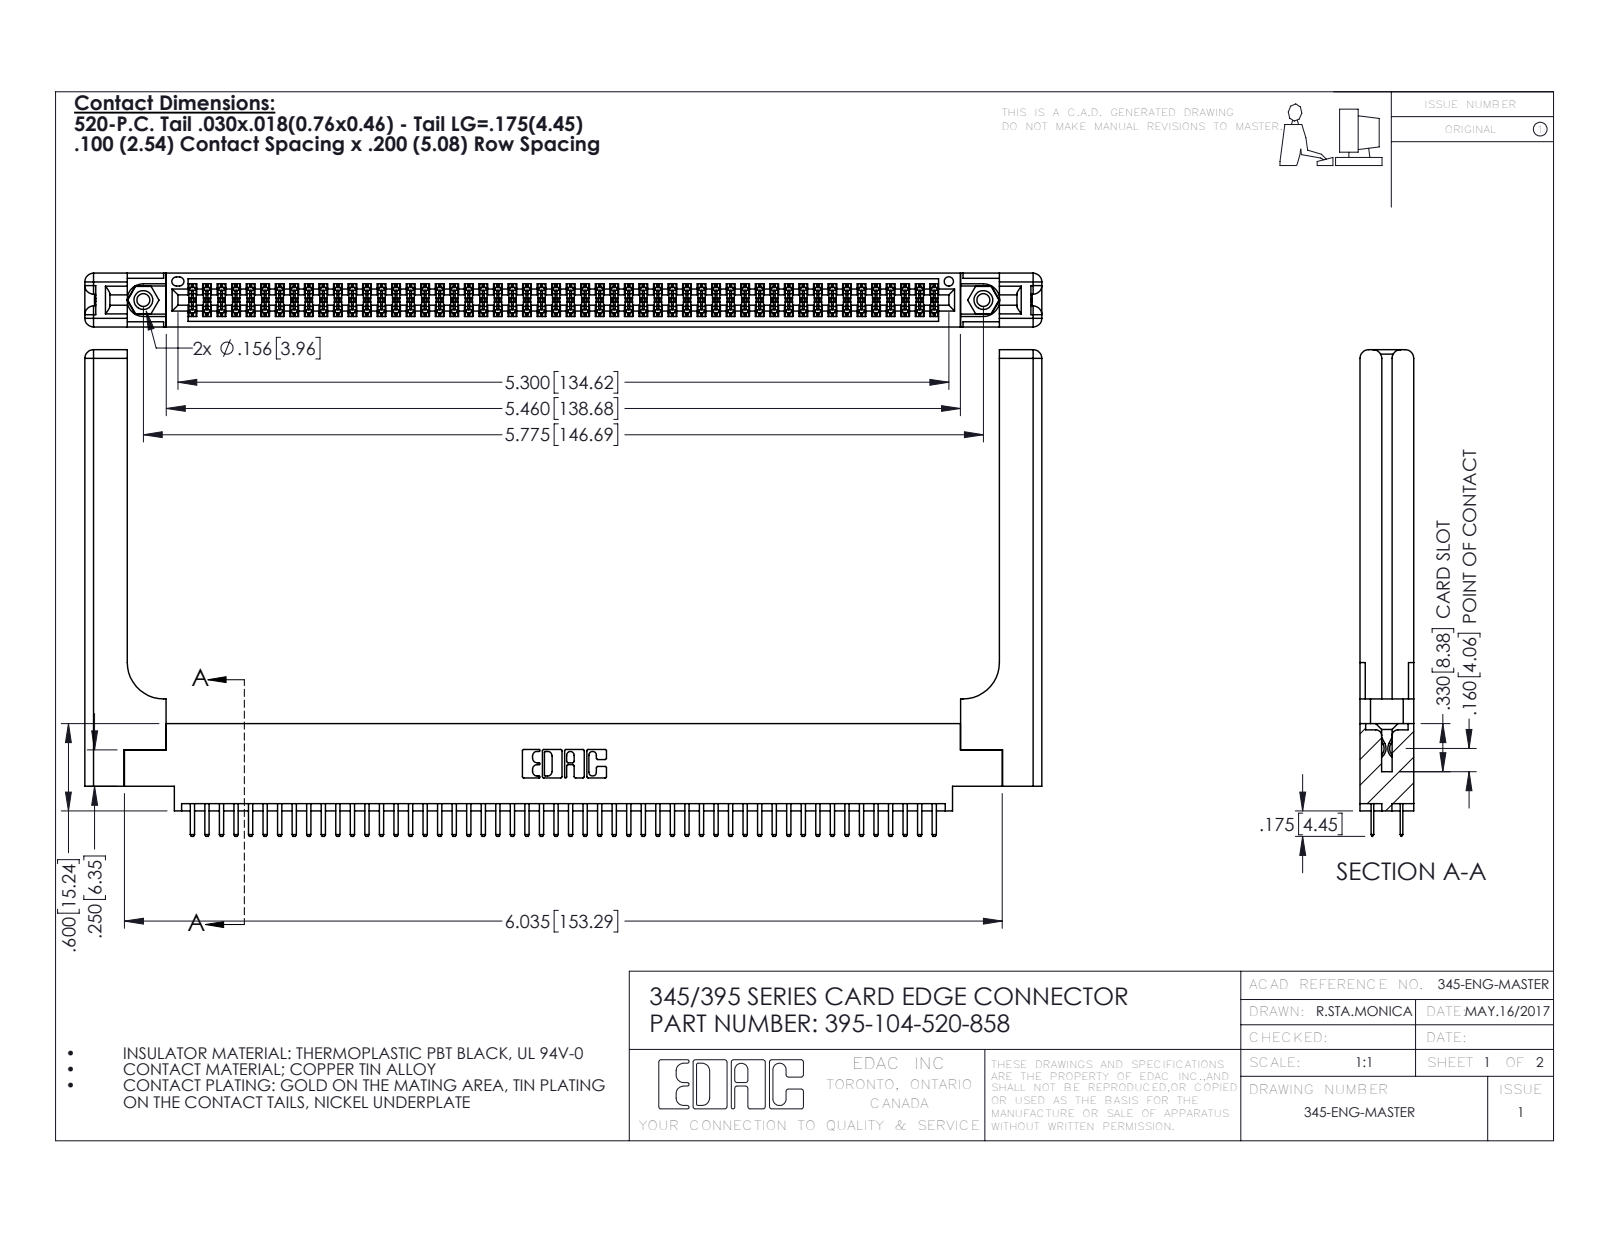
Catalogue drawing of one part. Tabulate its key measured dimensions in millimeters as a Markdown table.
| quantity | value |
| --- | --- |
| part name | 395-104-520-858; 345-250-001_345-250-001-102; 345-220-058_345-220-058; 345-292-001_345-293-120 (+1 more) |
| STEP written by | SolidWorks 2016 (CONFIG_CONTROL_DESIGN) |
| units | millimeters |
| bodies | 109 solids, 6002 faces (3872 planar, 2070 cylindrical, 60 other) |
| overall size | 167.1 × 85 × 9.4 |
| volume | 24 650 mm³ |
| surface area | 29 190 mm² |
| round holes (diameter × count) | 2.3 × 2, 3.2 × 2, 4 × 2, 1.6 × 1 |
| round bosses / shafts (diameter × count) | 3.9 × 2 |
| partial cylindrical surfaces (radius × count) | 0.2 × 156, 0.3 × 108, 0.3 × 22, 1.5 × 16, 0.2 × 6, 0.8 × 6, 0.7 × 3, 0.4 × 2 |
| main face-to-face distances | 1.8, 9.4, 7.6, 5.1, 2.5, 6.9, 0.6, 5.7, 3.8, 3.8 |
| hole center spacings | 6.9, 140.7, 146.7 |
